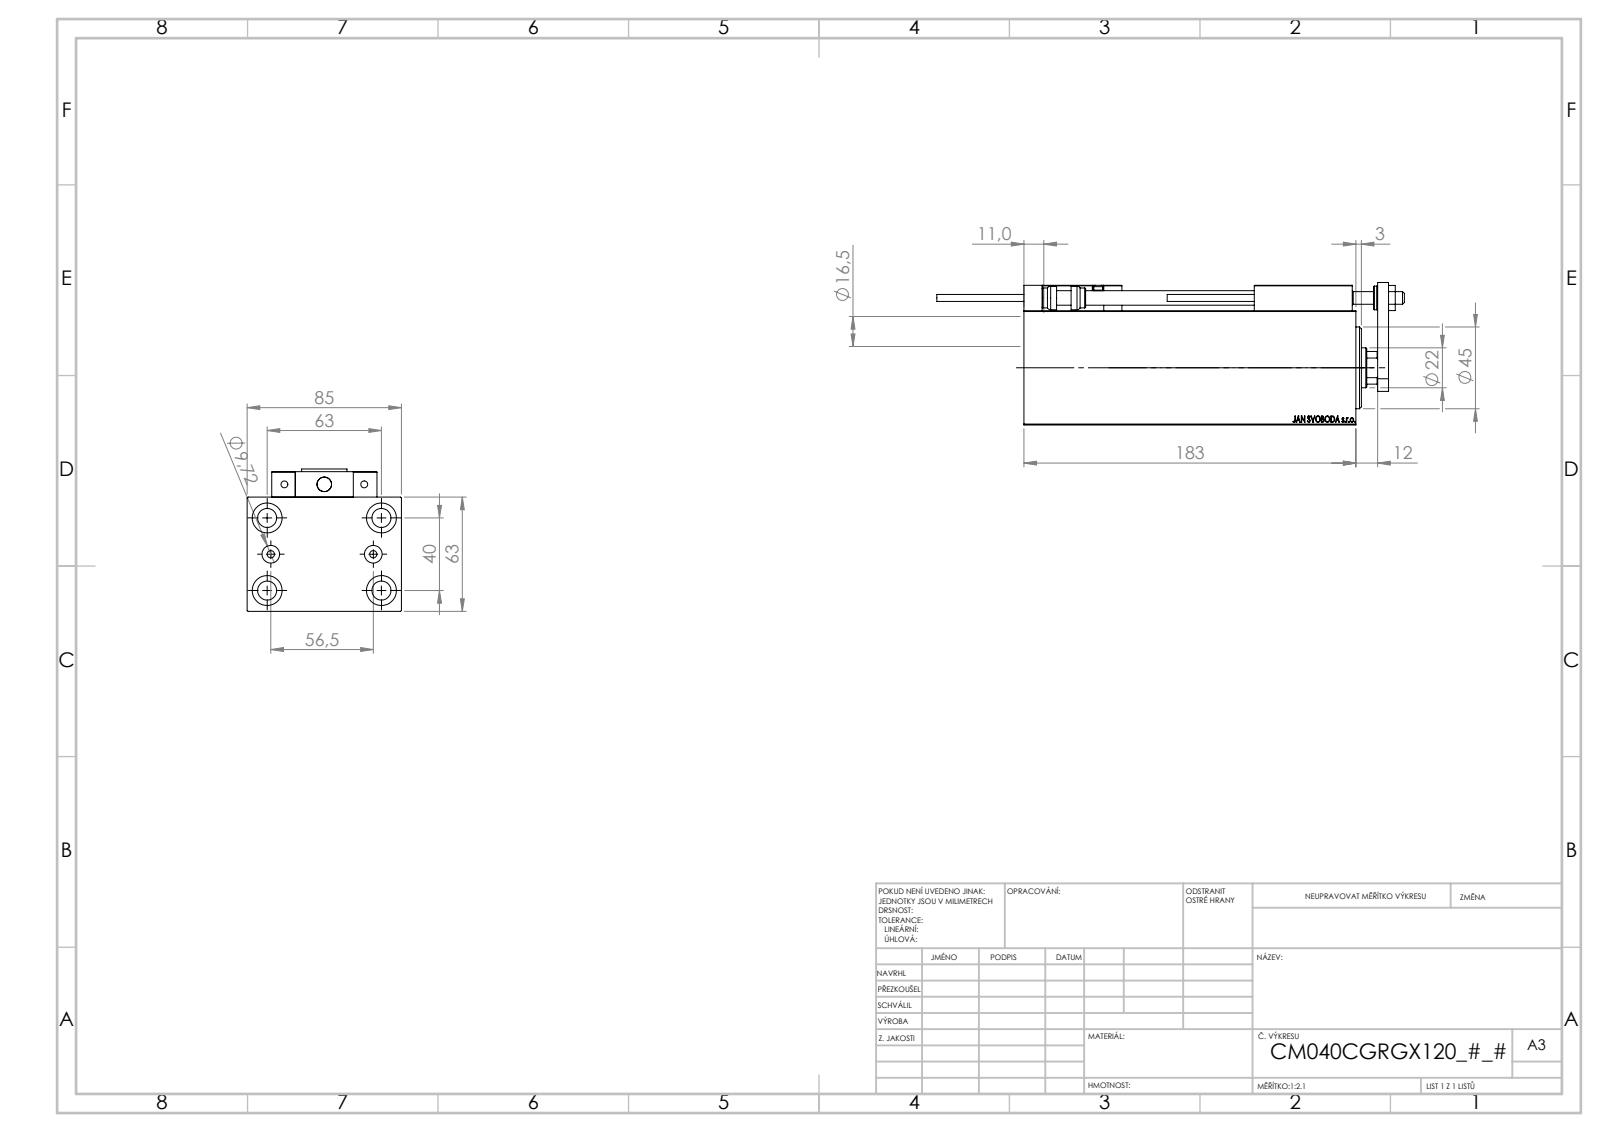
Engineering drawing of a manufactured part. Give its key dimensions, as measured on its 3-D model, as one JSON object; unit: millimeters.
{"part_name": "V450CM_VC_B; V450CM_C_Body; MAGNET; SWITCH_X_FRONT_BACK (+7 more)", "step_written_by": "SolidWorks 2019 (CONFIG_CONTROL_DESIGN)", "units": "millimeters", "bodies": {"solids": 23, "faces": 1278, "planar": 560, "cylindrical": 184, "other": 534}, "overall_size": [257.7, 85, 78.5], "volume_mm3": 852758, "surface_area_mm2": 169351, "round_holes": [[4, 6], [8, 5], [16.5, 5], [3.2, 4], [10.5, 4], [5, 2], [9.72, 2], [7, 1], [12.5, 1], [22, 1], [25.5, 1], [40, 1]], "round_bosses_or_shafts": [[5, 2], [3.8, 2], [13, 1], [11, 1]], "partial_cylinders_radius": [[0.3, 30], [3, 2], [10.5, 1]], "face_to_face_distances": [63, 85, 12, 183, 171, 14, 77, 18, 6, 1], "hole_center_spacings": [20.26, 37.31, 63.01, 11.37, 20, 28.25, 29.59, 29.69]}
